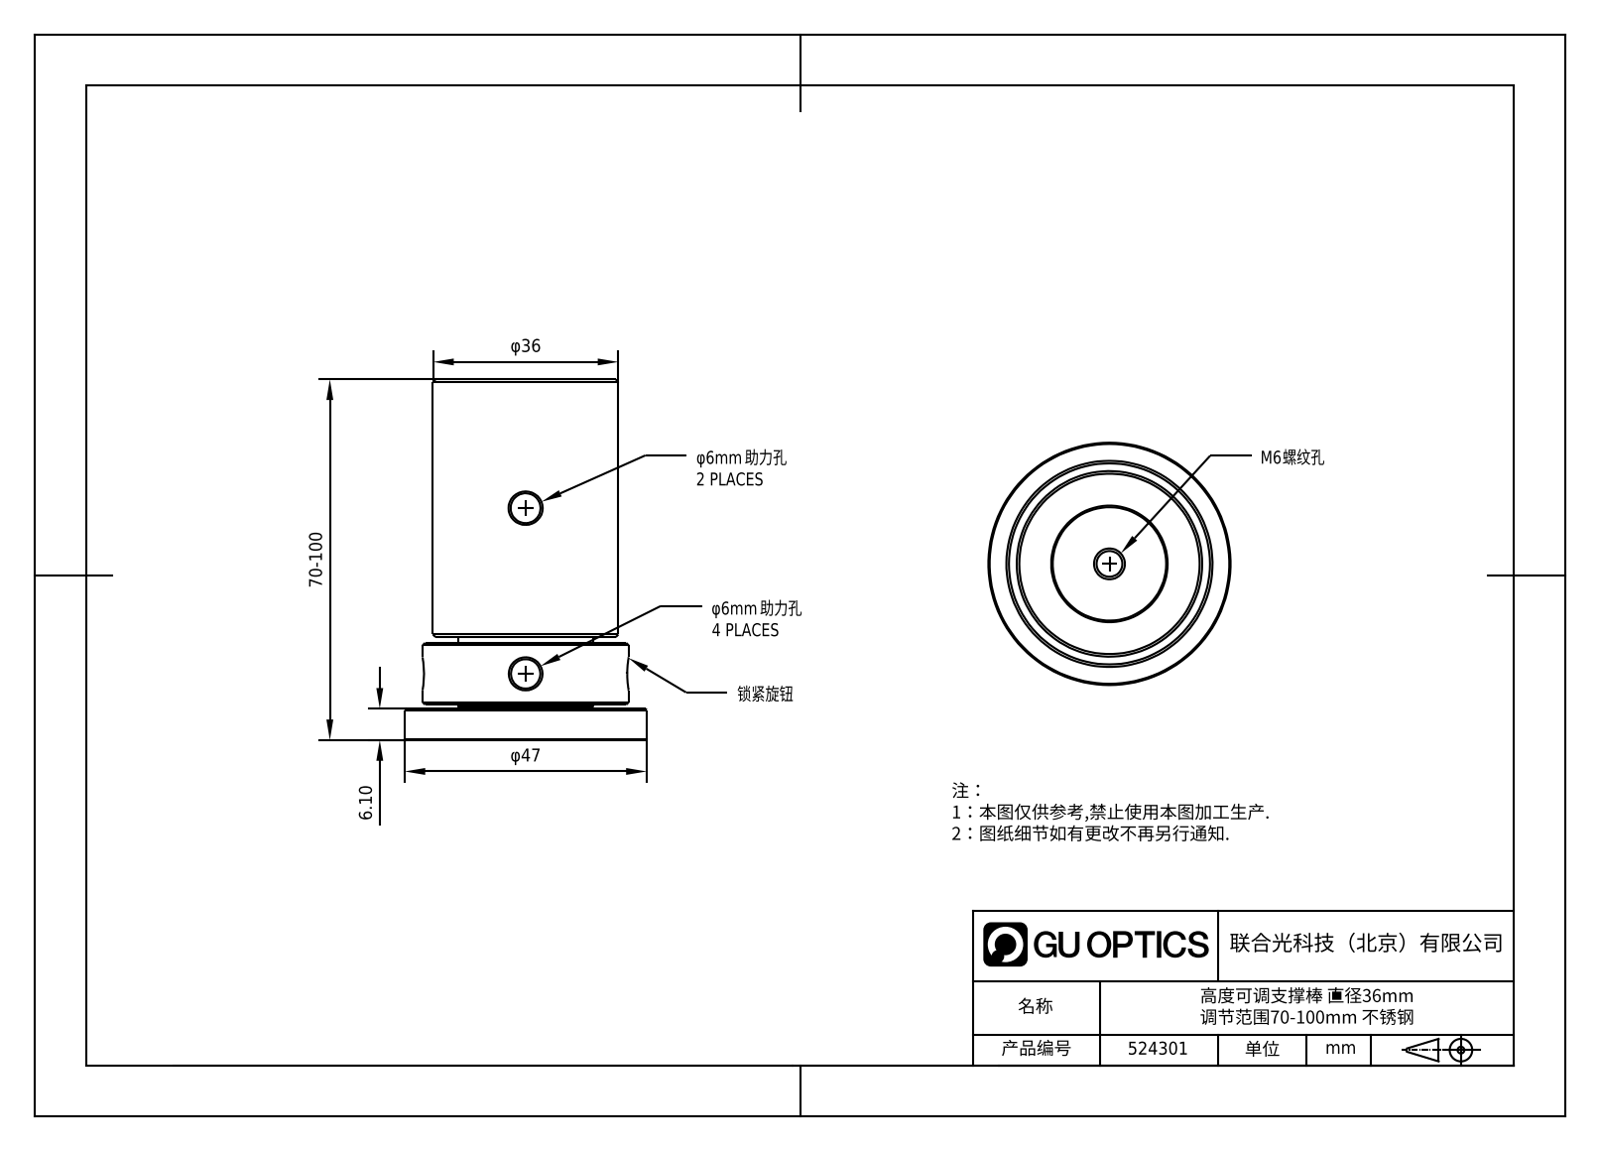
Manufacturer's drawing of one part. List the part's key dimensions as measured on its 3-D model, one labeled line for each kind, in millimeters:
Part name (STEP PRODUCT): 7.6.4.2_调整高度70-100mm，Rev.A; 1.4.6.3_ZGD-1.5B，1.5英寸支杆底座，带M6x6mm螺丝，A; 7.6.4.1.3，1.5英寸高度可调支杆滚花旋钮，带SM1内螺纹，Rev.A; 1.5英寸高度可调支杆立柱，带SM1外螺纹，Rev.A_7.6.4.2.2_1.5英寸可调支撑杆立柱，带SM1外螺纹，长度49mm (+1 more)
STEP written by: SolidWorks 2021 (CONFIG_CONTROL_DESIGN)
Units: millimetres
Bodies: 4 solids, 117 faces (23 planar, 36 cylindrical, 58 other)
Overall size (bounding box): 79.82 × 47 × 47
Volume: 76 374 mm³ · Surface area: 24 957 mm²
Round holes (diameter × count): ⌀5.7 ×3, ⌀5 ×1, ⌀5.8 ×1, ⌀25.4 ×1, ⌀26.4 ×1
Round bosses / shafts (diameter × count): ⌀47 ×1, ⌀40 ×1, ⌀36 ×1, ⌀26.29 ×1, ⌀6 ×1
Main face-to-face distances: 6.1, 18.1, 12, 0.5, 79.82, 73.72, 61.72, 66.32, 60.22, 48.22
